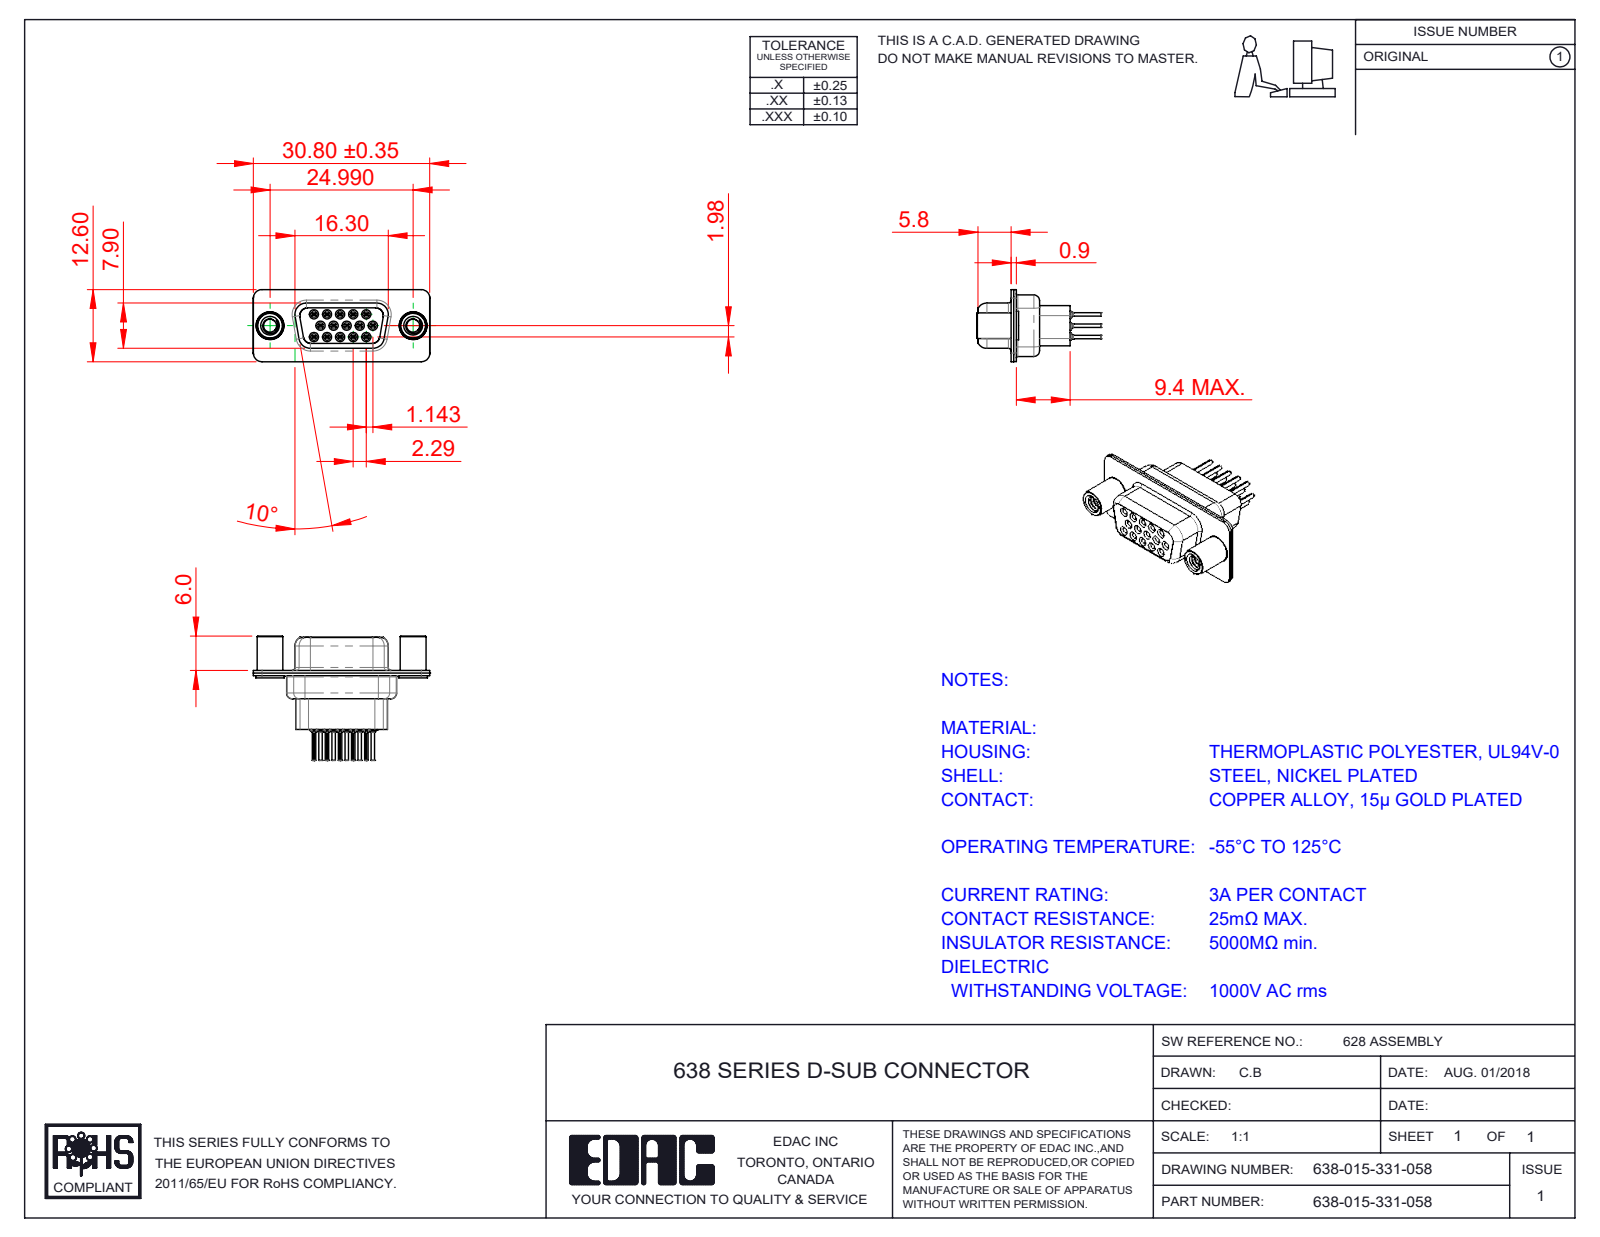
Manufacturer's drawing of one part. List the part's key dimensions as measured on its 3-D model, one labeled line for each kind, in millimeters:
Part name (STEP PRODUCT): 638 Shell Front_15 Contacts; 638 Shell Rear_15 Contacts; 638-015-331-058; 638 Contact Row 1_31 (+4 more)
STEP written by: SolidWorks 2020 (CONFIG_CONTROL_DESIGN)
Units: millimetres
Bodies: 20 solids, 2158 faces (534 planar, 660 cylindrical, 964 other)
Overall size (bounding box): 30.81 × 21.7 × 12.6
Volume: 1 946 mm³ · Surface area: 6 724 mm²
Round holes (diameter × count): ⌀0.2 ×15, ⌀0.8 ×15, ⌀1 ×15, ⌀1.1 ×15, ⌀1.6 ×15, ⌀1.7 ×15, ⌀1.8 ×15, ⌀2 ×2, ⌀2.26 ×2, ⌀4 ×2, ⌀4.05 ×2, ⌀4.85 ×2
Round bosses / shafts (diameter × count): ⌀2 ×15, ⌀1.5 ×15, ⌀1.2 ×15, ⌀0.6 ×15, ⌀5 ×2, ⌀4.95 ×2, ⌀4.8 ×2, ⌀4.5 ×2
Partial cylindrical surfaces — rounded edges, fillets, slot ends (radius × count): R0.1 ×30, R1.5 ×20, R2 ×12, R0.28 ×10, R1.55 ×8, R1.35 ×5, R0.25 ×4, R0.5 ×4
Main face-to-face distances: 0.45, 0.9, 0.4, 1.43, 8.88, 6.6, 7, 2.28, 0.85, 5.8
Hole centre spacings: 3.96, 2.28, 4.57, 2.29, 6.05, 6.04, 6.86, 7.92
